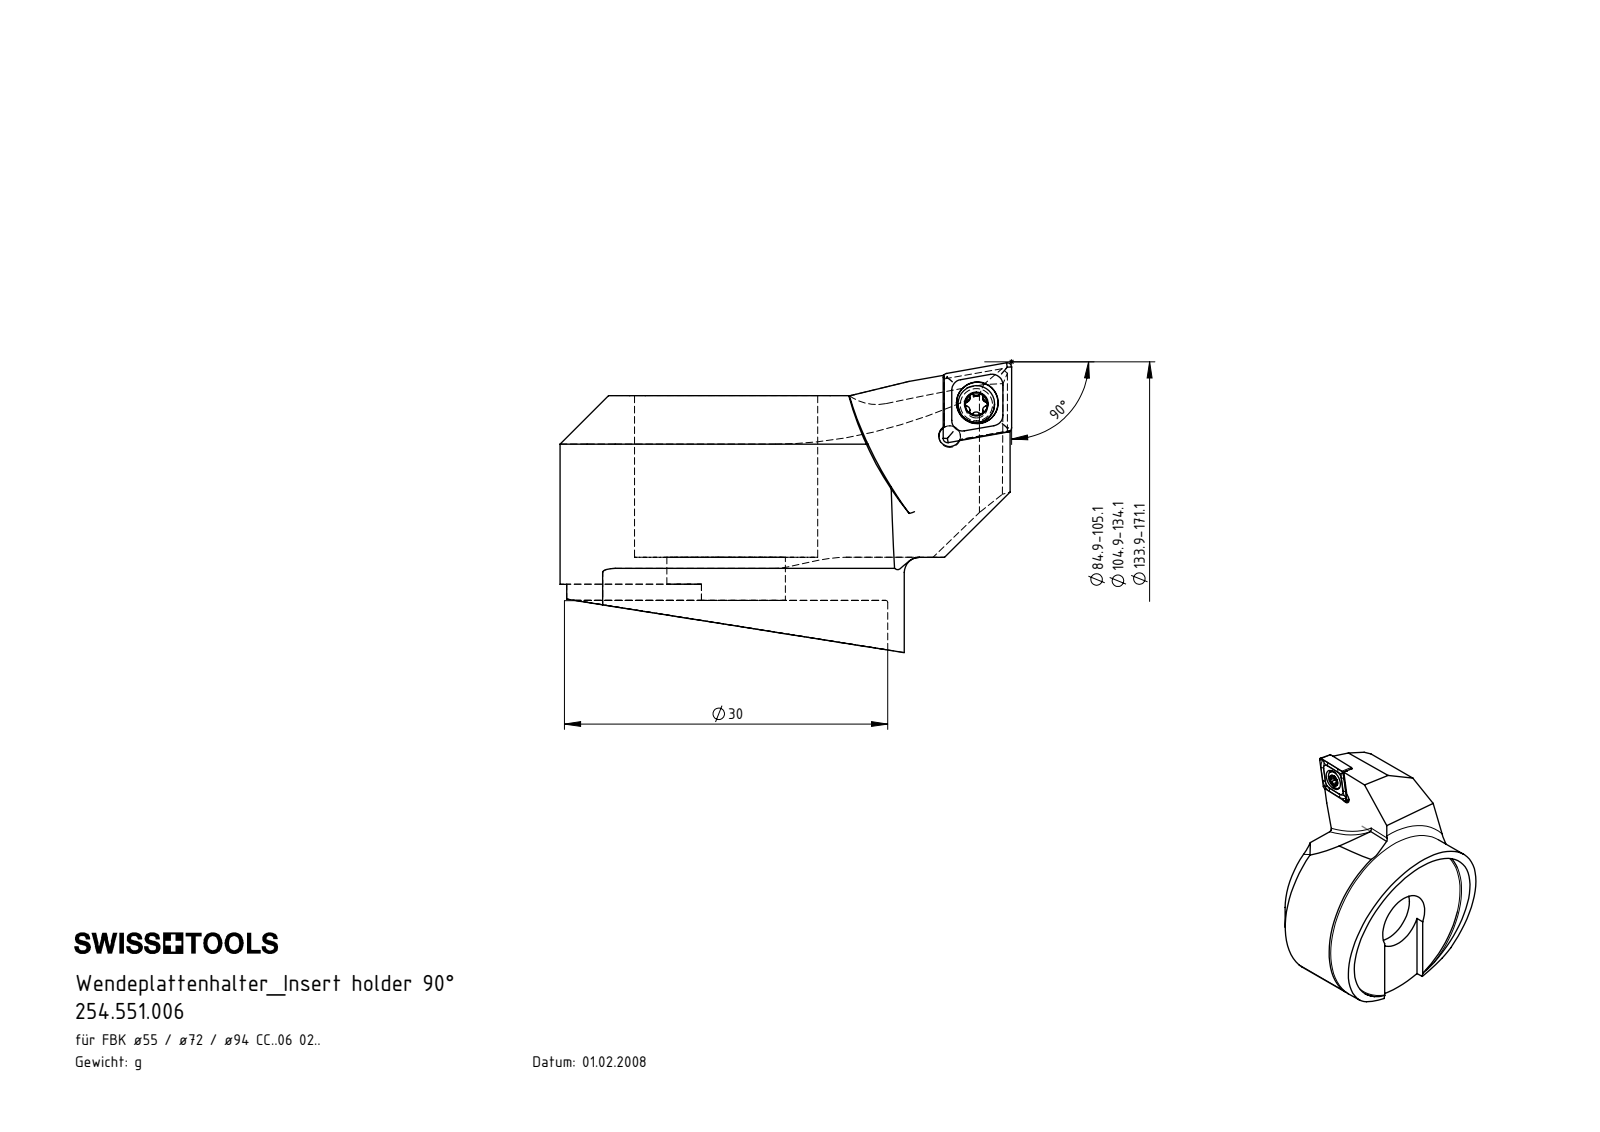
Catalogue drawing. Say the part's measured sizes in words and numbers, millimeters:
The part is named "254.551.006; F55-WCA.001.022_D_fertigbearbeitet; CCMT060204; WCA-ER2.001.006_A". Its 3-D file was written by "SolidWorks 2017 (CONFIG_CONTROL_DESIGN)". It is 5 solids with 161 faces: 50 planar, 51 cylindrical and 60 other. Overall it measures 41.9 by 33.2 by 26.89 millimeters. Its volume is 13 693 cubic millimeters and its surface area 5 984 square millimeters. Round holes: 1 of diameter 2, 1 of diameter 2.05, 1 of diameter 2.8, 1 of diameter 3.85, 1 of diameter 11, 1 of diameter 17, 1 of diameter 30. Round bosses or shafts: 1 of diameter 3.4, 1 of diameter 2.5. Partial cylindrical surfaces (rounded edges, fillets, slot ends): 6 of radius 0.21, 5 of radius 0.36, 2 of radius 0.5, 2 of radius 10, 1 of radius 0.36, 1 of radius 5, 1 of radius 16.55, 1 of radius 16.6. The main face-to-face distances are 19, 1, 18, 15, 14, 4, 1.5, 17.5, 16.5, 2.5. The hole center spacings are 3.86, 4.01.
